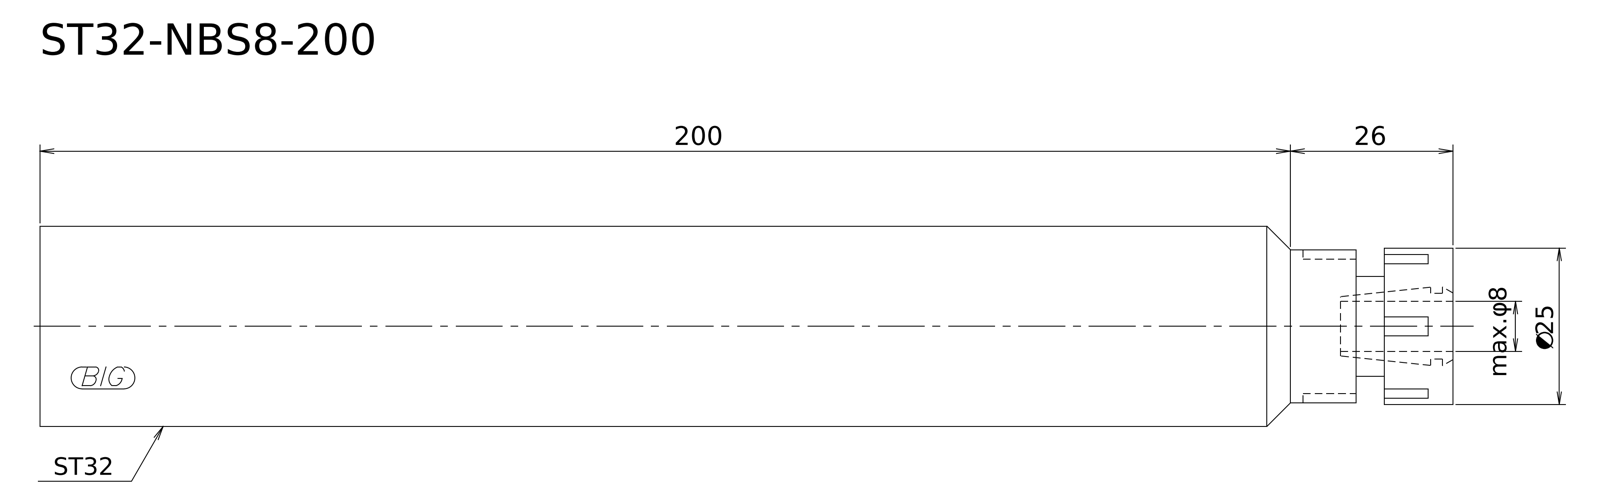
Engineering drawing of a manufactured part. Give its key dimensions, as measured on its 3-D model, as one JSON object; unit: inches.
{"step_written_by": "Kubotek KeyCreator V8.5.1 (14335) (CONFIG_CONTROL_DESIGN)", "units": "inches", "bodies": {"solids": 1, "faces": 9, "planar": 4, "cylindrical": 4, "other": 1}, "overall_size": [8.898, 1.26, 1.26], "volume_in3": 10.46, "surface_area_in2": 37.13, "round_bosses_or_shafts": [[1.26, 1], [0.984, 1], [0.965, 1], [0.63, 1]], "face_to_face_distances": [8.898, 0.433, 8.465, 0.61, 0.177, 8.287]}
